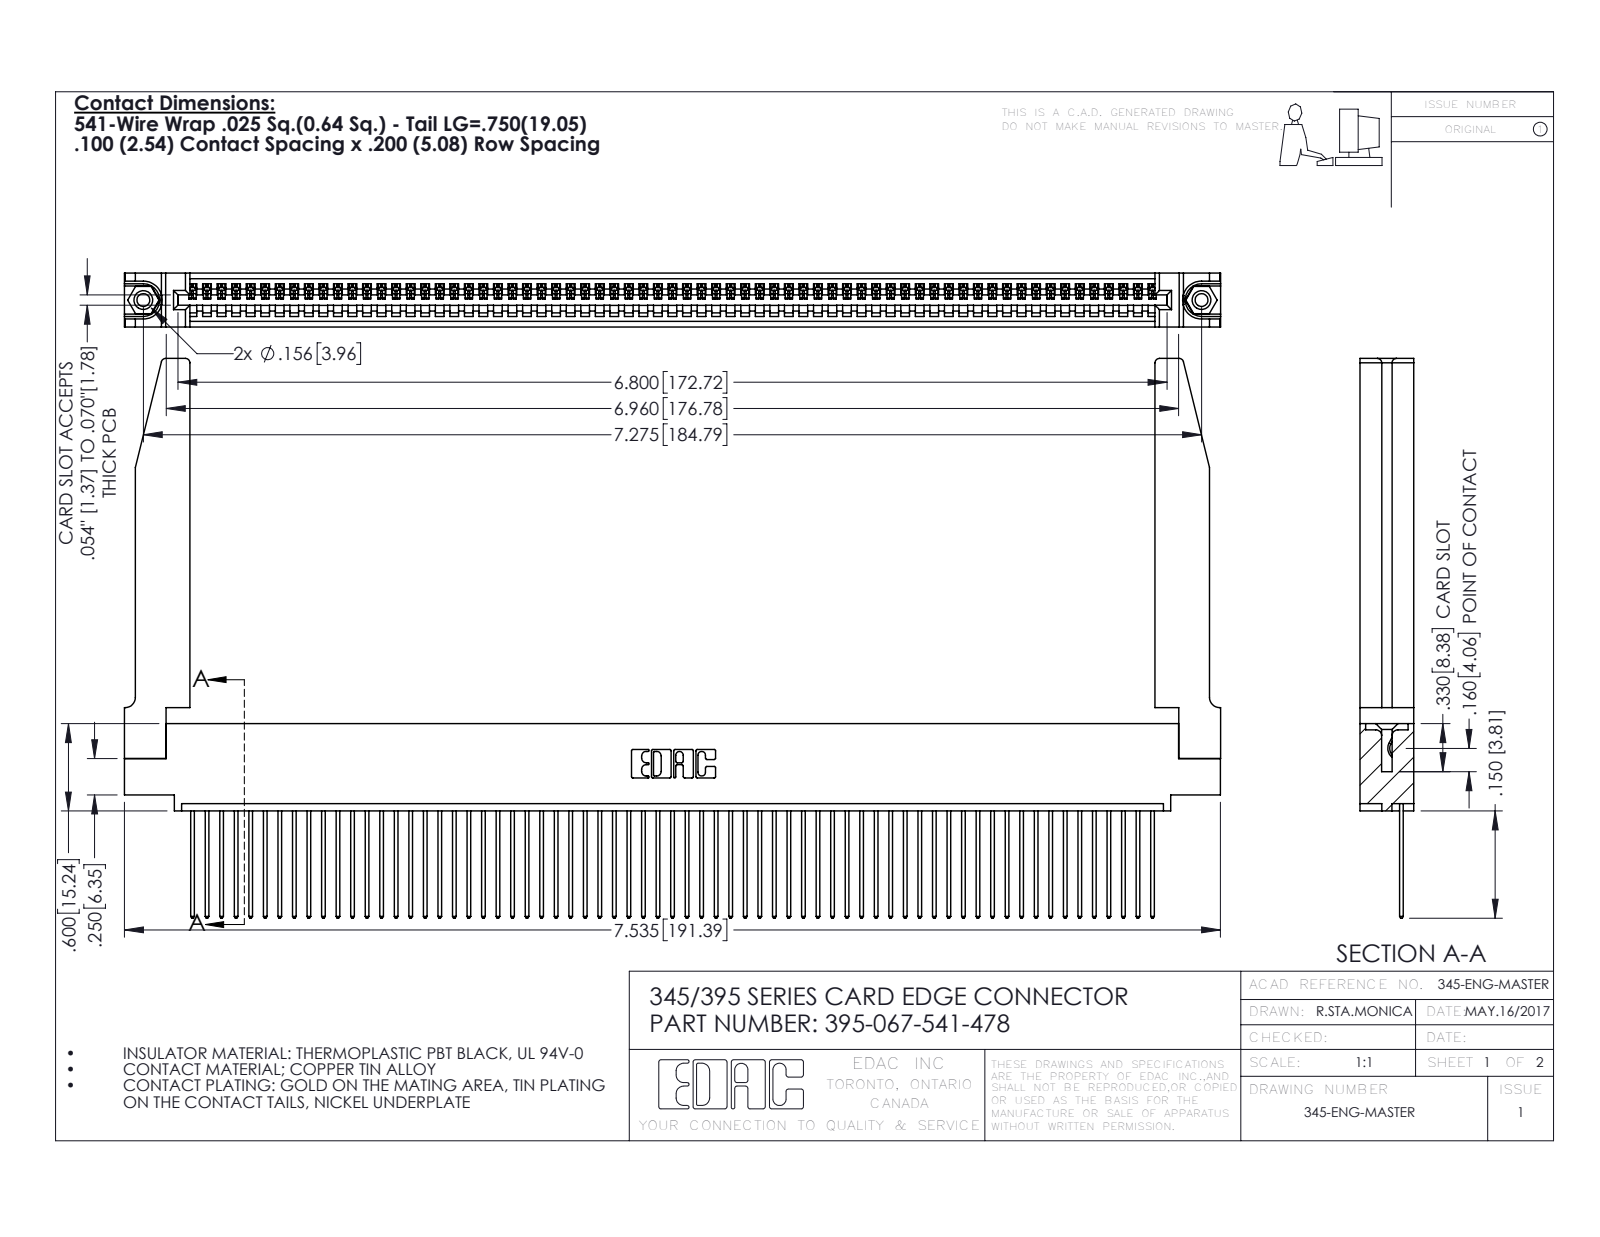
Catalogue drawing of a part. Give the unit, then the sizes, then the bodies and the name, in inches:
Units: inches
Overall size (bounding box): 7.536 × 3.847 × 0.37
Round holes (diameter × count): ⌀0.089 ×2, ⌀0.125 ×2, ⌀0.156 ×2, ⌀0.064 ×1
Round bosses / shafts (diameter × count): ⌀0.155 ×2
Partial cylindrical surfaces — rounded edges, fillets, slot ends (radius × count): R0.006 ×134, R0.01 ×134, R0.01 ×22, R0.03 ×8, R0.007 ×6, R0.031 ×6, R0.026 ×3, R0.031 ×2
Main face-to-face distances: 0.072, 0.298, 0.37, 0.098, 0.272, 0.025, 0.2, 0.225, 0.149, 0.148
Hole centre spacings: 0.27, 7.039, 7.275
Volume: 1.605 in³ · Surface area: 51.46 in²
Bodies: 72 solids, 4250 faces (2906 planar, 1292 cylindrical, 52 other)
Part name (STEP PRODUCT): 395-067-541-478; 345-250-001_345-250-001-102; 345-292-001_345-293-141; 345-220-078_345-220-078 (+1 more)
STEP written by: SolidWorks 2016 (CONFIG_CONTROL_DESIGN)
